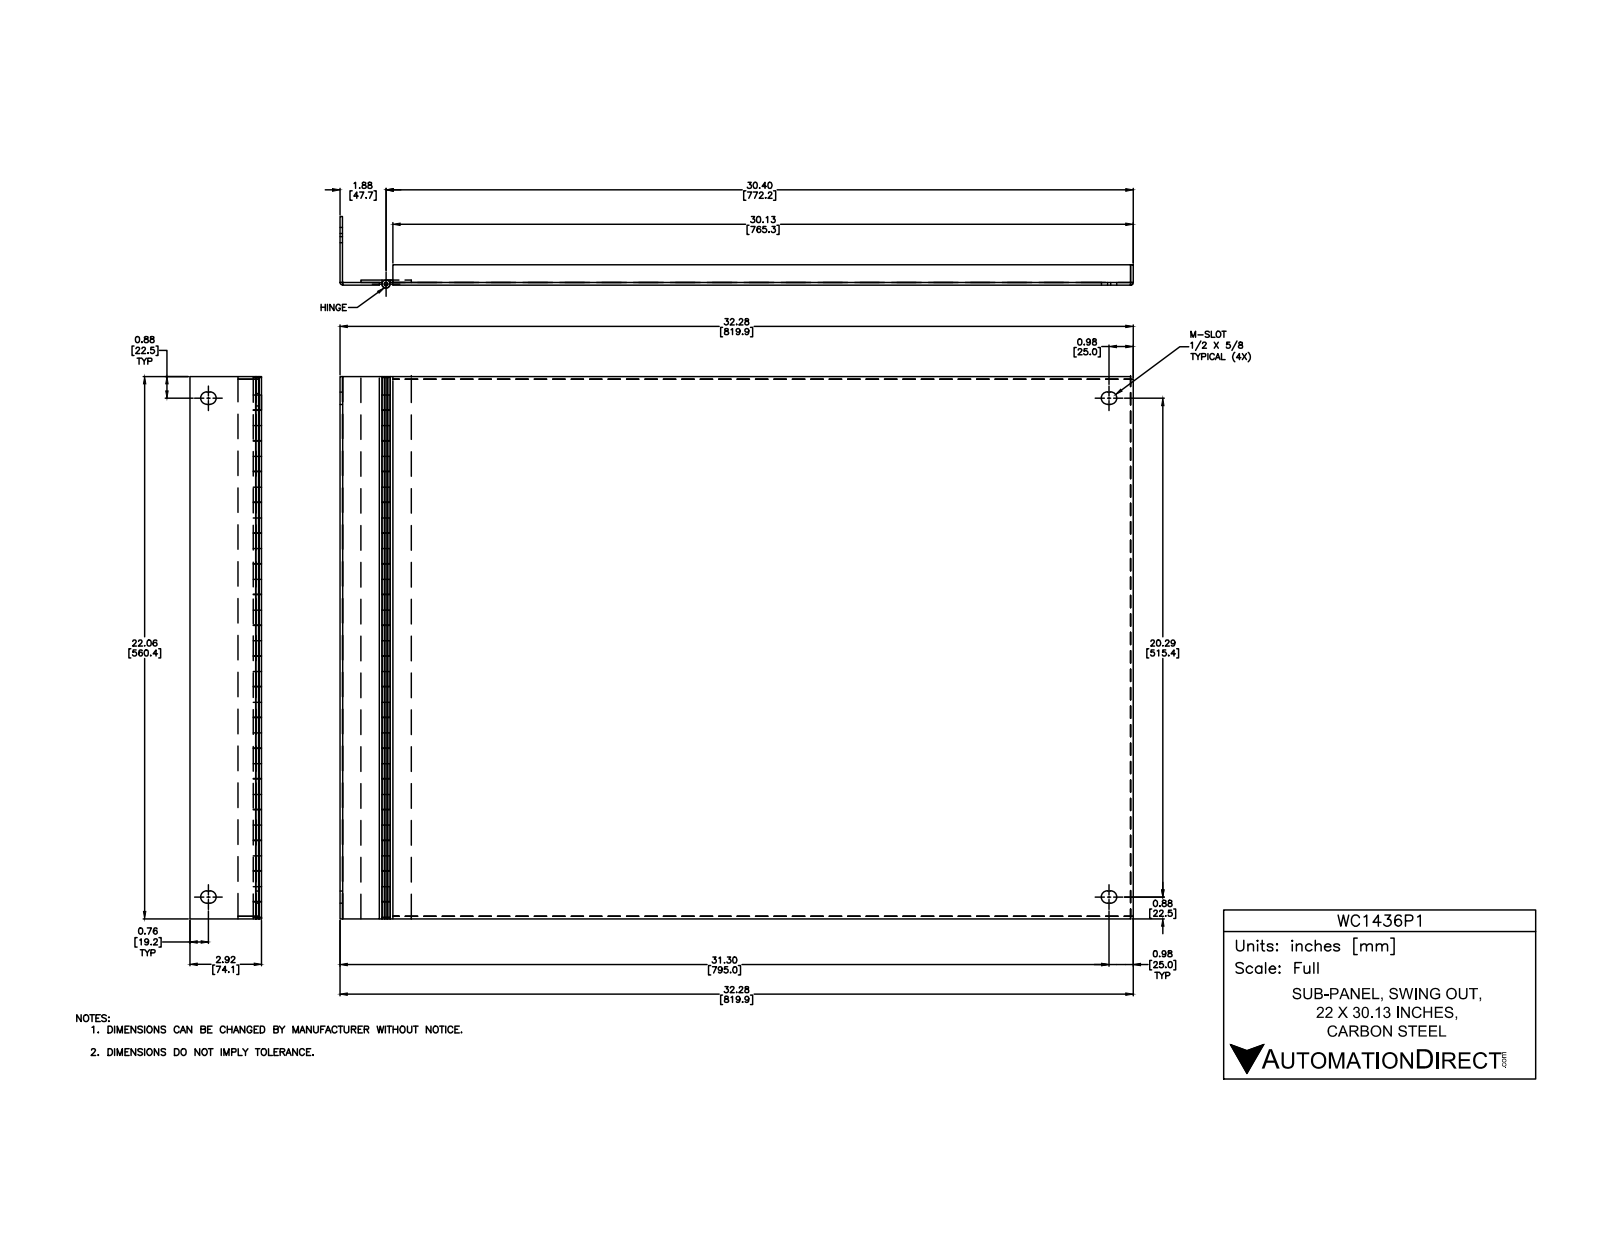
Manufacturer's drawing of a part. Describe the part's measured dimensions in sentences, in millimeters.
The part is named "WC1436P1; WC1436P1_DOOR; WC1436P1_OUTHINGE; WC1436P1_INHINGE (+2 more)". Its 3-D file was written by "SolidWorks 2014 (AUTOMOTIVE_DESIGN)". It is 5 solids with 286 faces: 155 planar, 127 cylindrical and 4 other. Overall it measures 819.8 by 560.4 by 75.7 millimeters. Its volume is 1 495 000 cubic millimeters and its surface area 1 148 000 square millimeters. Round holes: 1 of diameter 3.7. Round bosses or shafts: 1 of diameter 8.5, 1 of diameter 3.2. Partial cylindrical surfaces (rounded edges, fillets, slot ends): 8 of radius 6.4, 3 of radius 2.7, 1 of radius 2.7. The main face-to-face distances are 2.7, 2.6, 557.7, 5.3, 817.1, 560.4, 555.1, 819.8, 814.5, 15.8.
